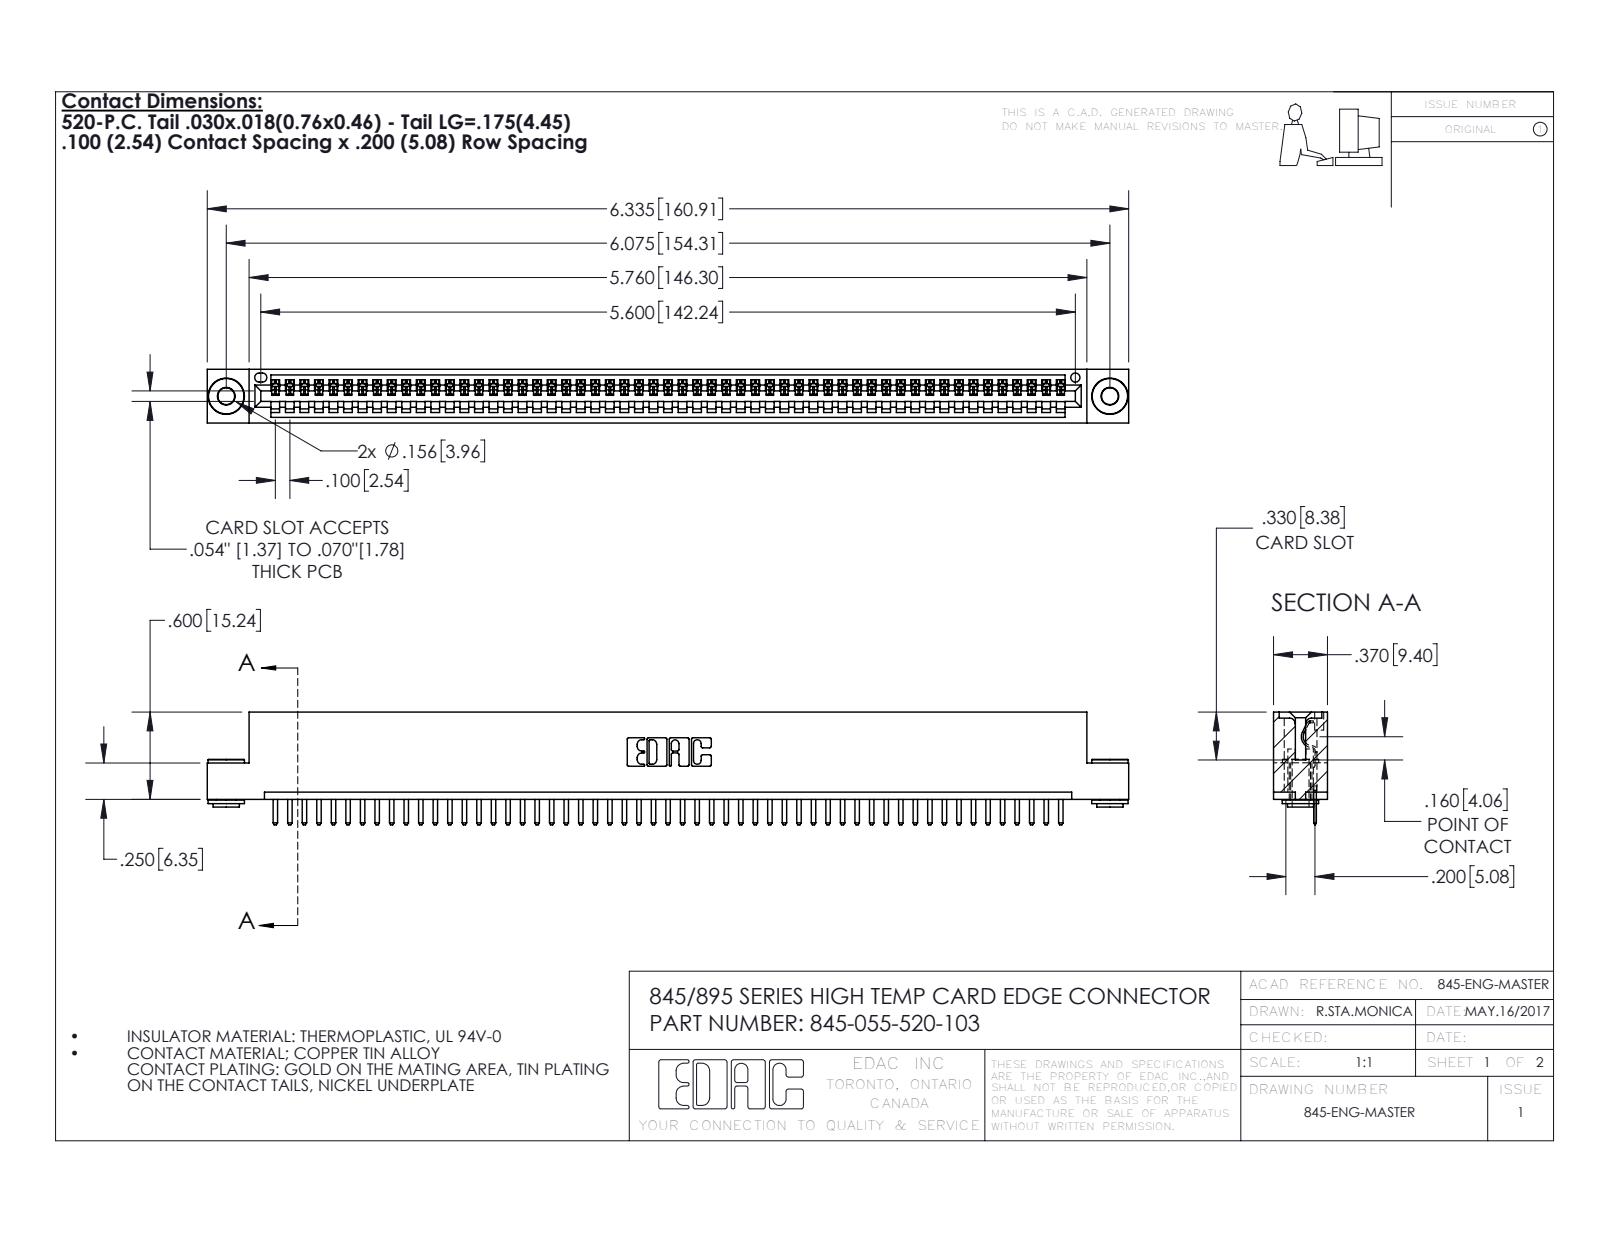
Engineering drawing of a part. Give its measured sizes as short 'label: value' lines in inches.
name: 345 Part_Flush Mounting Lugs - 0.156 Dia-TH; 345-250-002_345-250-002-102; 345-292-001_345-293-120; 345-055-520-103
written by: SolidWorks 2016 (CONFIG_CONTROL_DESIGN)
unit: in
bodies: 58 solids, 3574 faces (2400 planar, 1166 cylindrical, 8 other)
size: 6.335 × 0.775 × 0.37
volume: 0.931 in³; area: 31.22 in²
holes: 2× ⌀0.116, 2× ⌀0.156, 1× ⌀0.064
bosses: 2× ⌀0.25, 2× ⌀0.18, 2× ⌀0.136
rounds: 112× R0.01, 110× R0.006, 22× R0.01, 6× R0.007, 6× R0.031, 3× R0.026, 2× R0.031, 2× R0.04
face distances: 0.072, 0.298, 0.37, 0.2, 0.025, 0.098, 0.272, 0.225, 0.072, 0.149
hole spacings: 0.27, 5.839, 6.075
